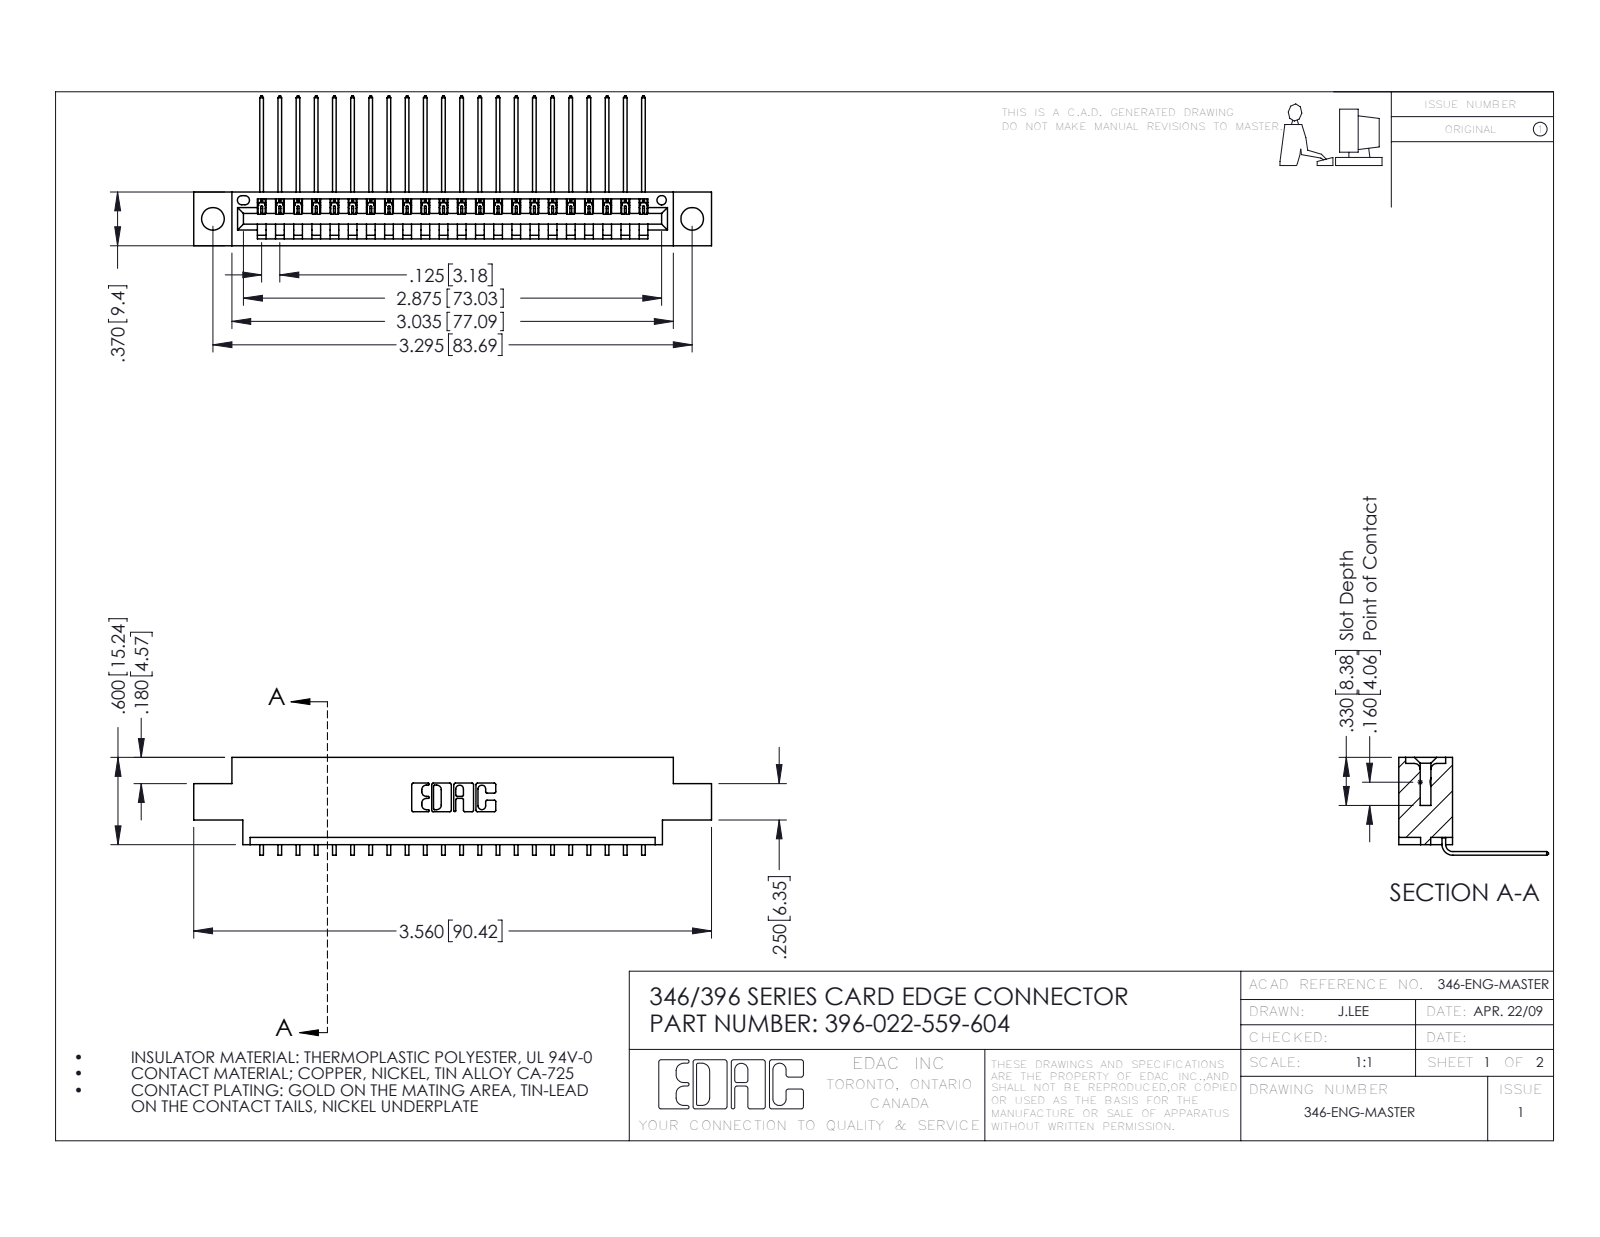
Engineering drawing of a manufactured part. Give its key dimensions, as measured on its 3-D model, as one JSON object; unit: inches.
{"part_name": "396-022-559-604; 345-292-001_558 559 Tail - 1; 346 Part_0.170 Offset - 0.156 Dia-TH", "step_written_by": "SolidWorks 2016 (CONFIG_CONTROL_DESIGN)", "units": "inches", "bodies": {"solids": 23, "faces": 1446, "planar": 1004, "cylindrical": 442, "other": 0}, "overall_size": [3.56, 1.03, 0.673], "volume_in3": 0.509, "surface_area_in2": 16.46, "round_holes": [[0.156, 2], [0.064, 1]], "partial_cylinders_radius": [[0.006, 44], [0.01, 22], [0.007, 6], [0.031, 6], [0.026, 3], [0.031, 2], [0.04, 2], [0.014, 1]], "face_to_face_distances": [0.048, 0.322, 0.37, 0.25, 0.025, 0.072, 0.148, 0.222, 0.1, 0.174], "hole_center_spacings": [0.246, 3.087, 3.295]}
